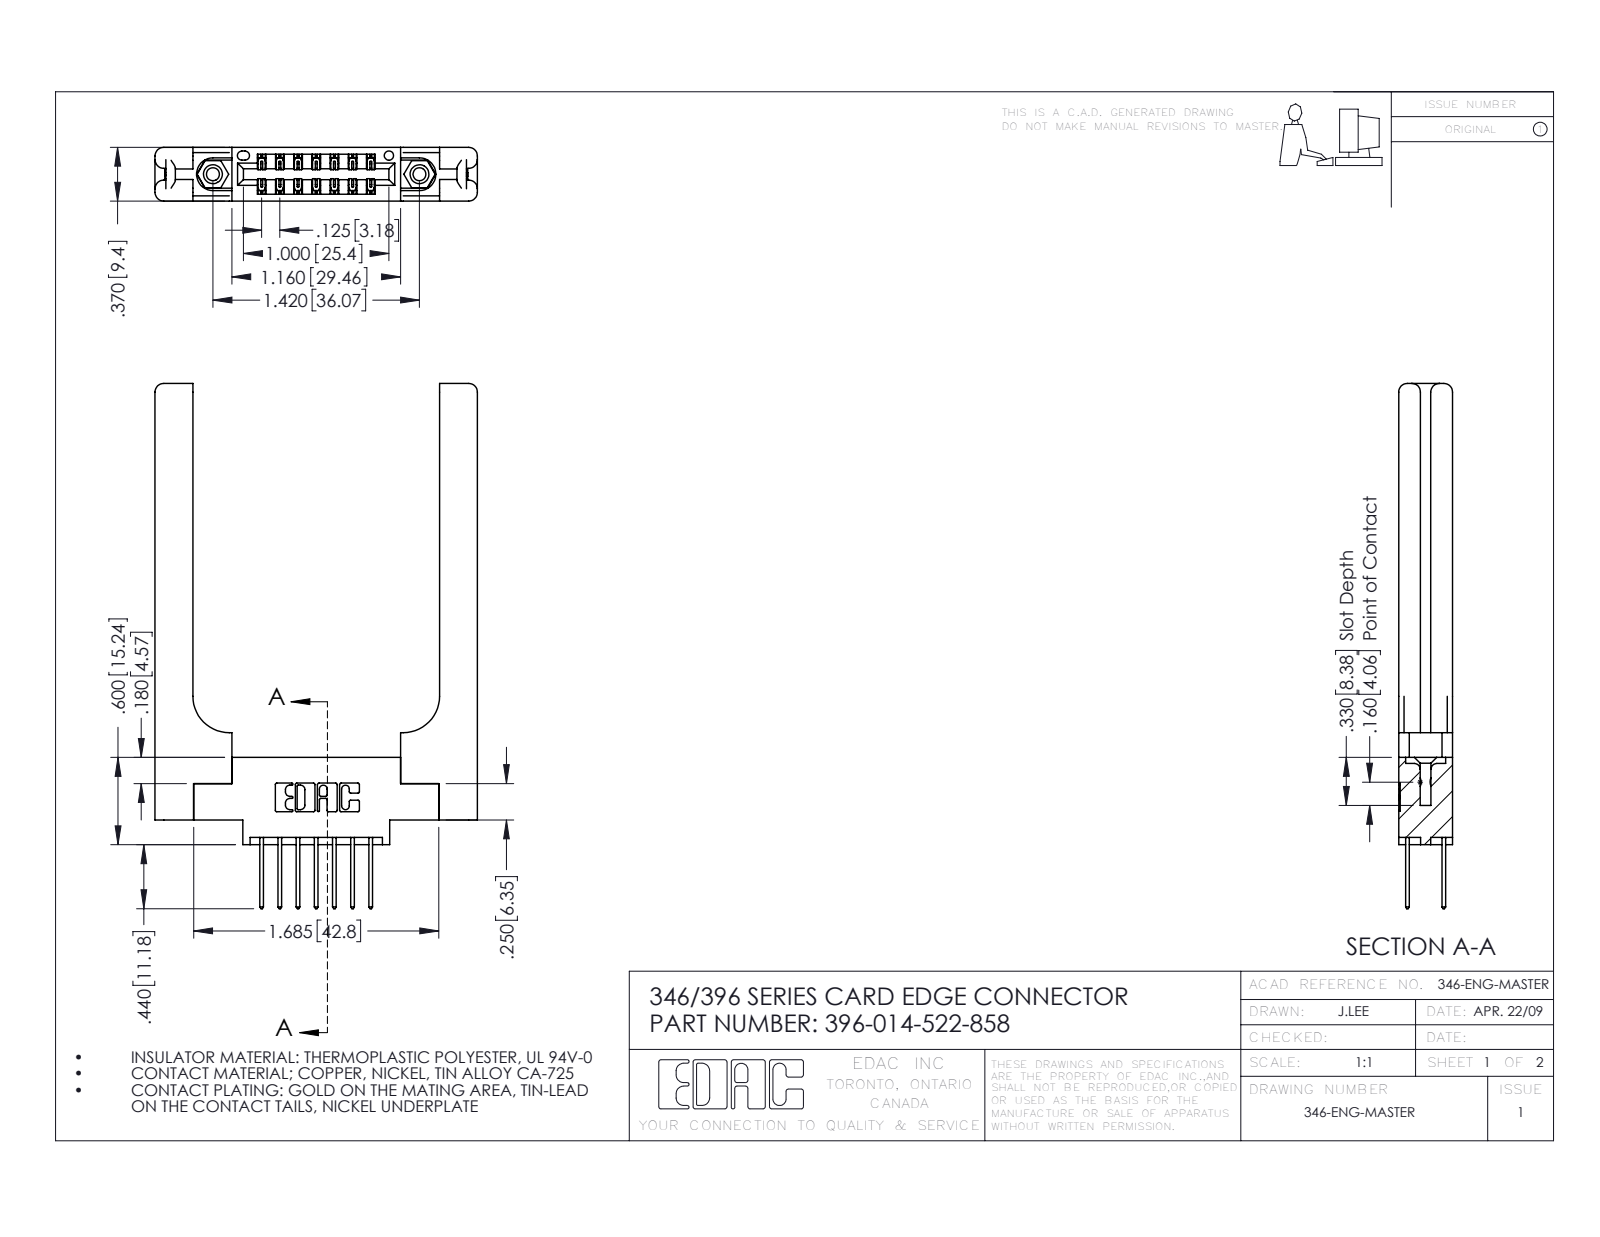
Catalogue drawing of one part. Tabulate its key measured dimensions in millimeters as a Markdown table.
| quantity | value |
| --- | --- |
| part name | 345-292-001_345-293-122; 396-014-522-858; 346 Part_0.170 Offset - 0.156 Dia-TH; 346-220-058_345-220-058 (+1 more) |
| STEP written by | SolidWorks 2016 (CONFIG_CONTROL_DESIGN) |
| units | millimeters |
| bodies | 19 solids, 1110 faces (718 planar, 332 cylindrical, 60 other) |
| overall size | 91.7 × 56.3 × 9.4 |
| volume | 12 600 mm³ |
| surface area | 11 770 mm² |
| round holes (diameter × count) | 2.3 × 2, 3.2 × 2, 4 × 2, 1.6 × 1 |
| round bosses / shafts (diameter × count) | 3.9 × 2 |
| partial cylindrical surfaces (radius × count) | 0.3 × 22, 0.2 × 21, 1.5 × 16, 0.3 × 14, 0.2 × 6, 0.8 × 6, 0.7 × 3, 0.4 × 2 |
| main face-to-face distances | 9.4, 3.8, 5.6, 1.8, 3.8, 6.4, 2.6, 1.2, 8.2, 4.4 |
| hole center spacings | 6.2, 30.9, 36.1 |
